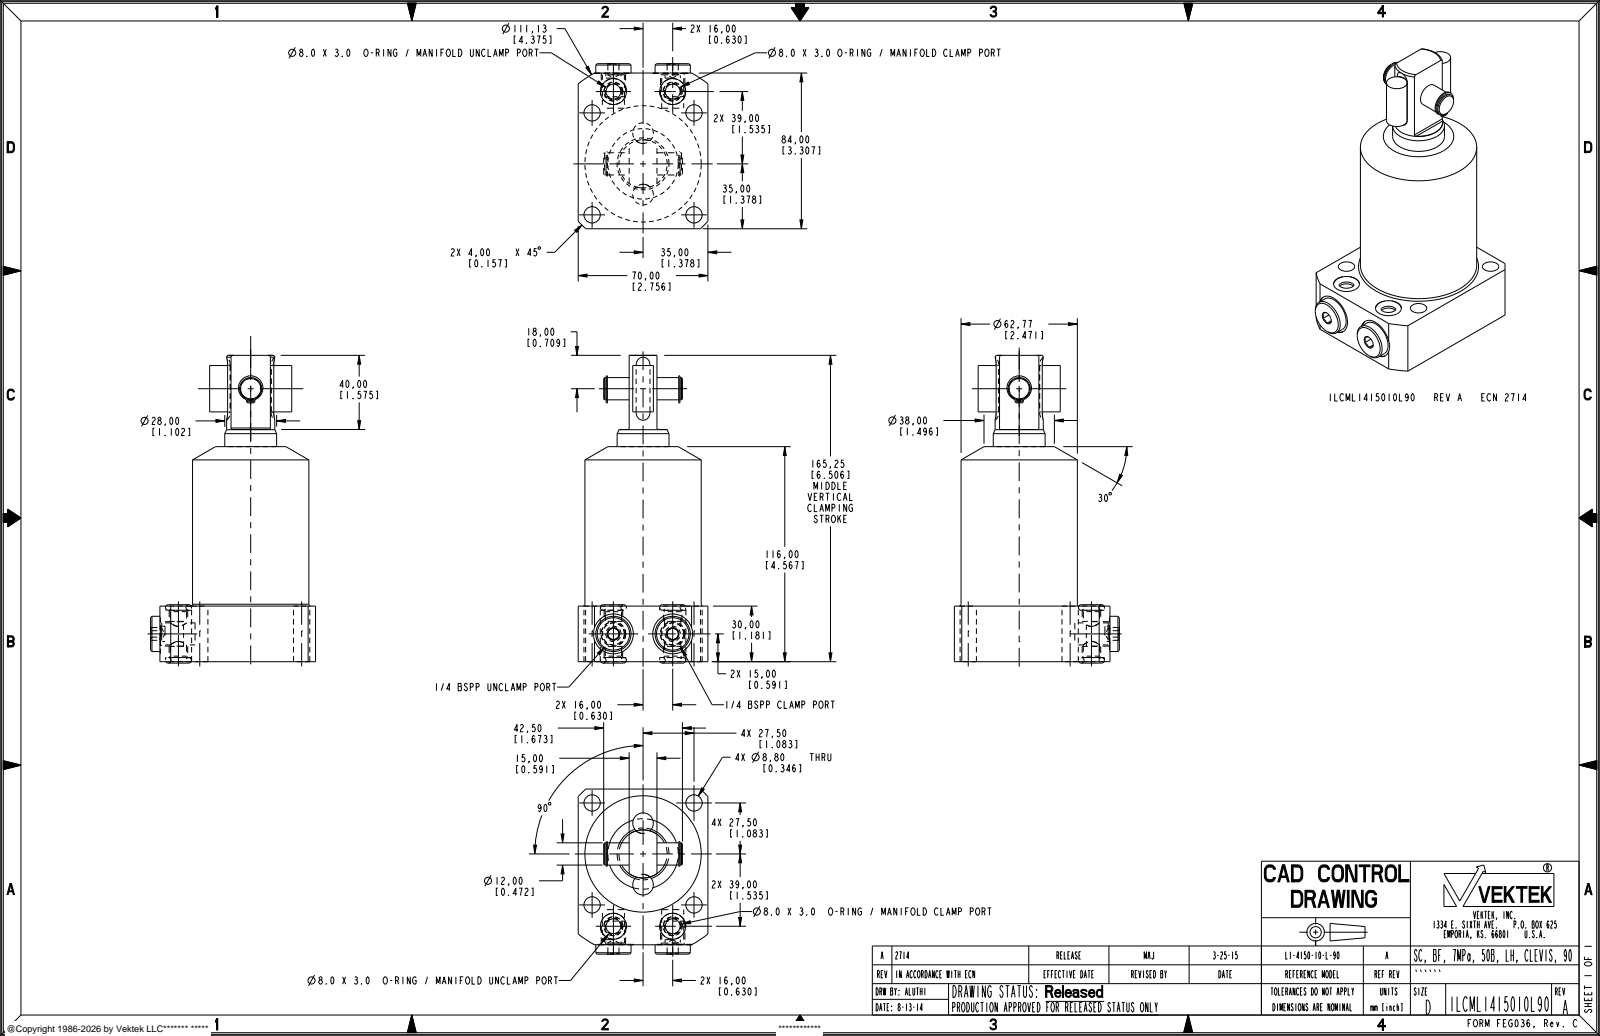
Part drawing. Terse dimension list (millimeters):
name: ILCML1415010L90
written by: PRO/ENGINEER BY PARAMETRIC TECHNOLOGY CORPORATION, 2013320 (AUTOMOTIVE_DESIGN)
unit: mm
bodies: 7 solids, 240 faces (80 planar, 96 cylindrical, 64 other)
size: 166 × 89.05 × 70
volume: 449 711 mm³; area: 52 993 mm²
holes: 4× ⌀8.8, 2× ⌀1.04, 2× ⌀8.75, 2× ⌀11.89, 2× ⌀14, 2× ⌀21.5
bosses: 2× ⌀19, 2× ⌀13.16, 2× ⌀11.12, 2× ⌀10, 2× ⌀8.25, 1× ⌀62.77, 1× ⌀28, 1× ⌀26
rounds: 2× R0.8, 2× R1.04, 2× R1.09, 2× R5.56, 1× R55.56
face distances: 70, 30, 42.5, 27.5, 84, 15, 116, 86, 89.05, 5.05
hole spacings: 55, 16.26, 32, 44.99, 67.49, 77.78, 79.46, 2.4
